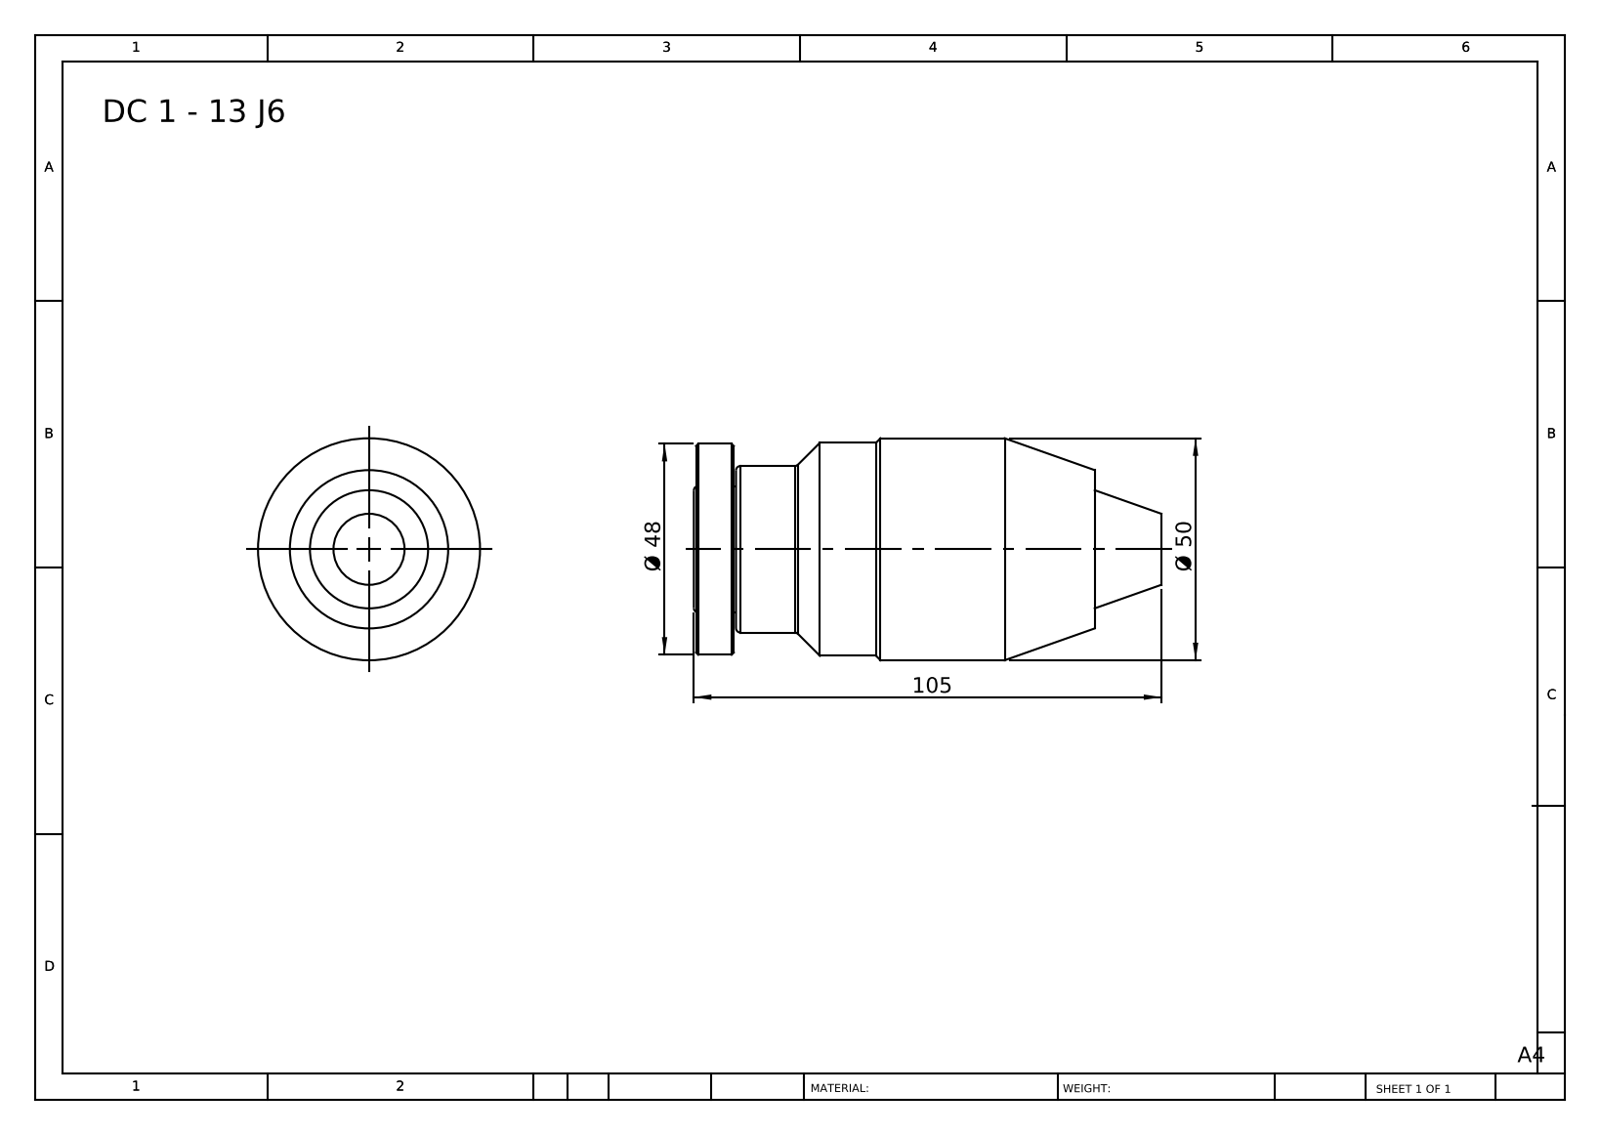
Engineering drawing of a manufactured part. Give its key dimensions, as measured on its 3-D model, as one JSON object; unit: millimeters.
{"part_name": "DC 1 - 13 B16", "step_written_by": "SolidWorks 2014 (CONFIG_CONTROL_DESIGN)", "units": "millimeters", "bodies": {"solids": 1, "faces": 42, "planar": 8, "cylindrical": 14, "other": 20}, "overall_size": [105.3, 50, 50], "volume_mm3": 152884, "surface_area_mm2": 19692, "round_holes": [[28.48, 1]], "round_bosses_or_shafts": [[50, 1], [48, 1], [47.5, 1], [37.5, 1], [28.47, 1]], "face_to_face_distances": [8.5, 0.5, 9, 81.3, 89.8, 90.3, 80.8, 9.5, 15, 95.8]}
